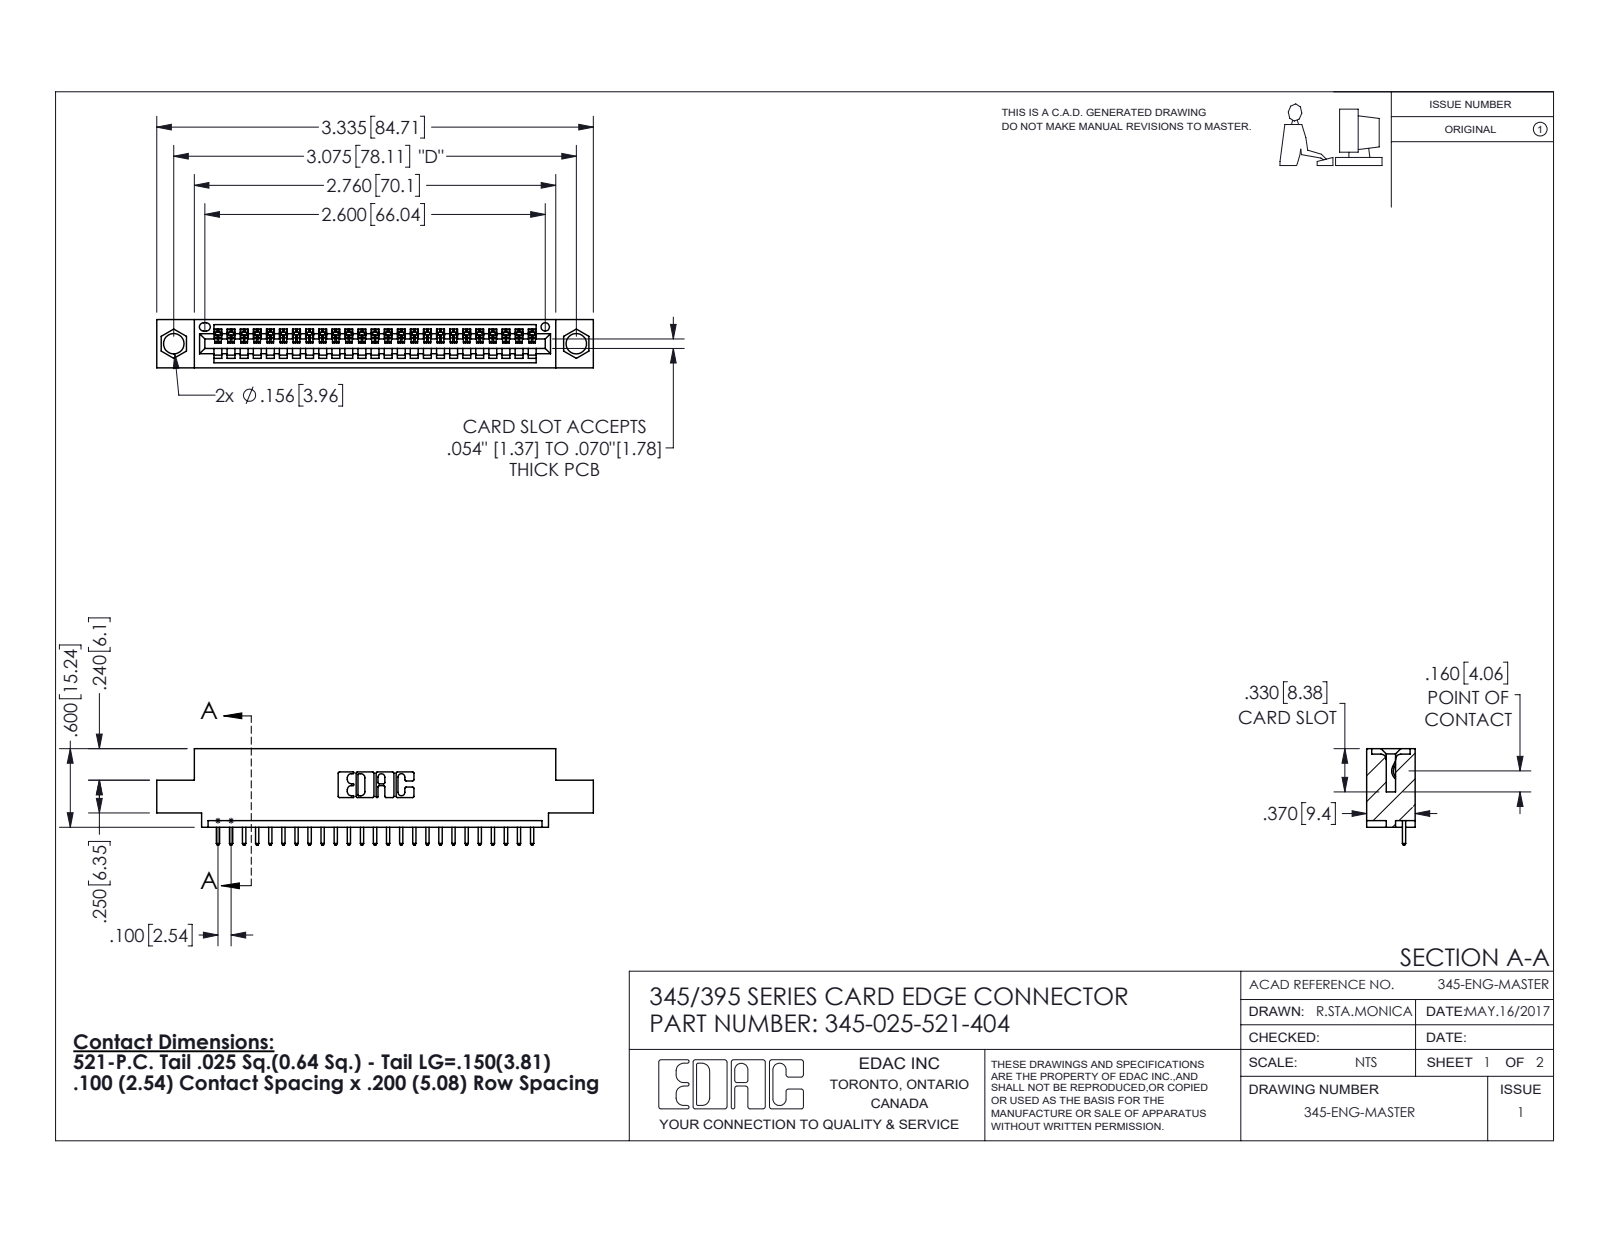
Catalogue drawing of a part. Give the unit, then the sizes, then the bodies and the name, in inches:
Units: inches
Overall size (bounding box): 3.335 × 0.737 × 0.37
Round holes (diameter × count): ⌀0.156 ×2, ⌀0.064 ×1
Partial cylindrical surfaces — rounded edges, fillets, slot ends (radius × count): R0.006 ×50, R0.01 ×50, R0.01 ×22, R0.007 ×6, R0.031 ×6, R0.026 ×3, R0.031 ×2, R0.04 ×2
Main face-to-face distances: 0.298, 0.072, 0.37, 0.2, 0.098, 0.272, 0.025, 0.225, 0.149, 0.072
Hole centre spacings: 0.27, 2.84, 3.075
Volume: 0.468 in³ · Surface area: 14.85 in²
Bodies: 26 solids, 1580 faces (1084 planar, 496 cylindrical, 0 other)
Part name (STEP PRODUCT): 345 Part_0.110 Offset - 0.156 Dia-TH; 345-025-521-404; 345-292-001_345-293-121
STEP written by: SolidWorks 2016 (CONFIG_CONTROL_DESIGN)
